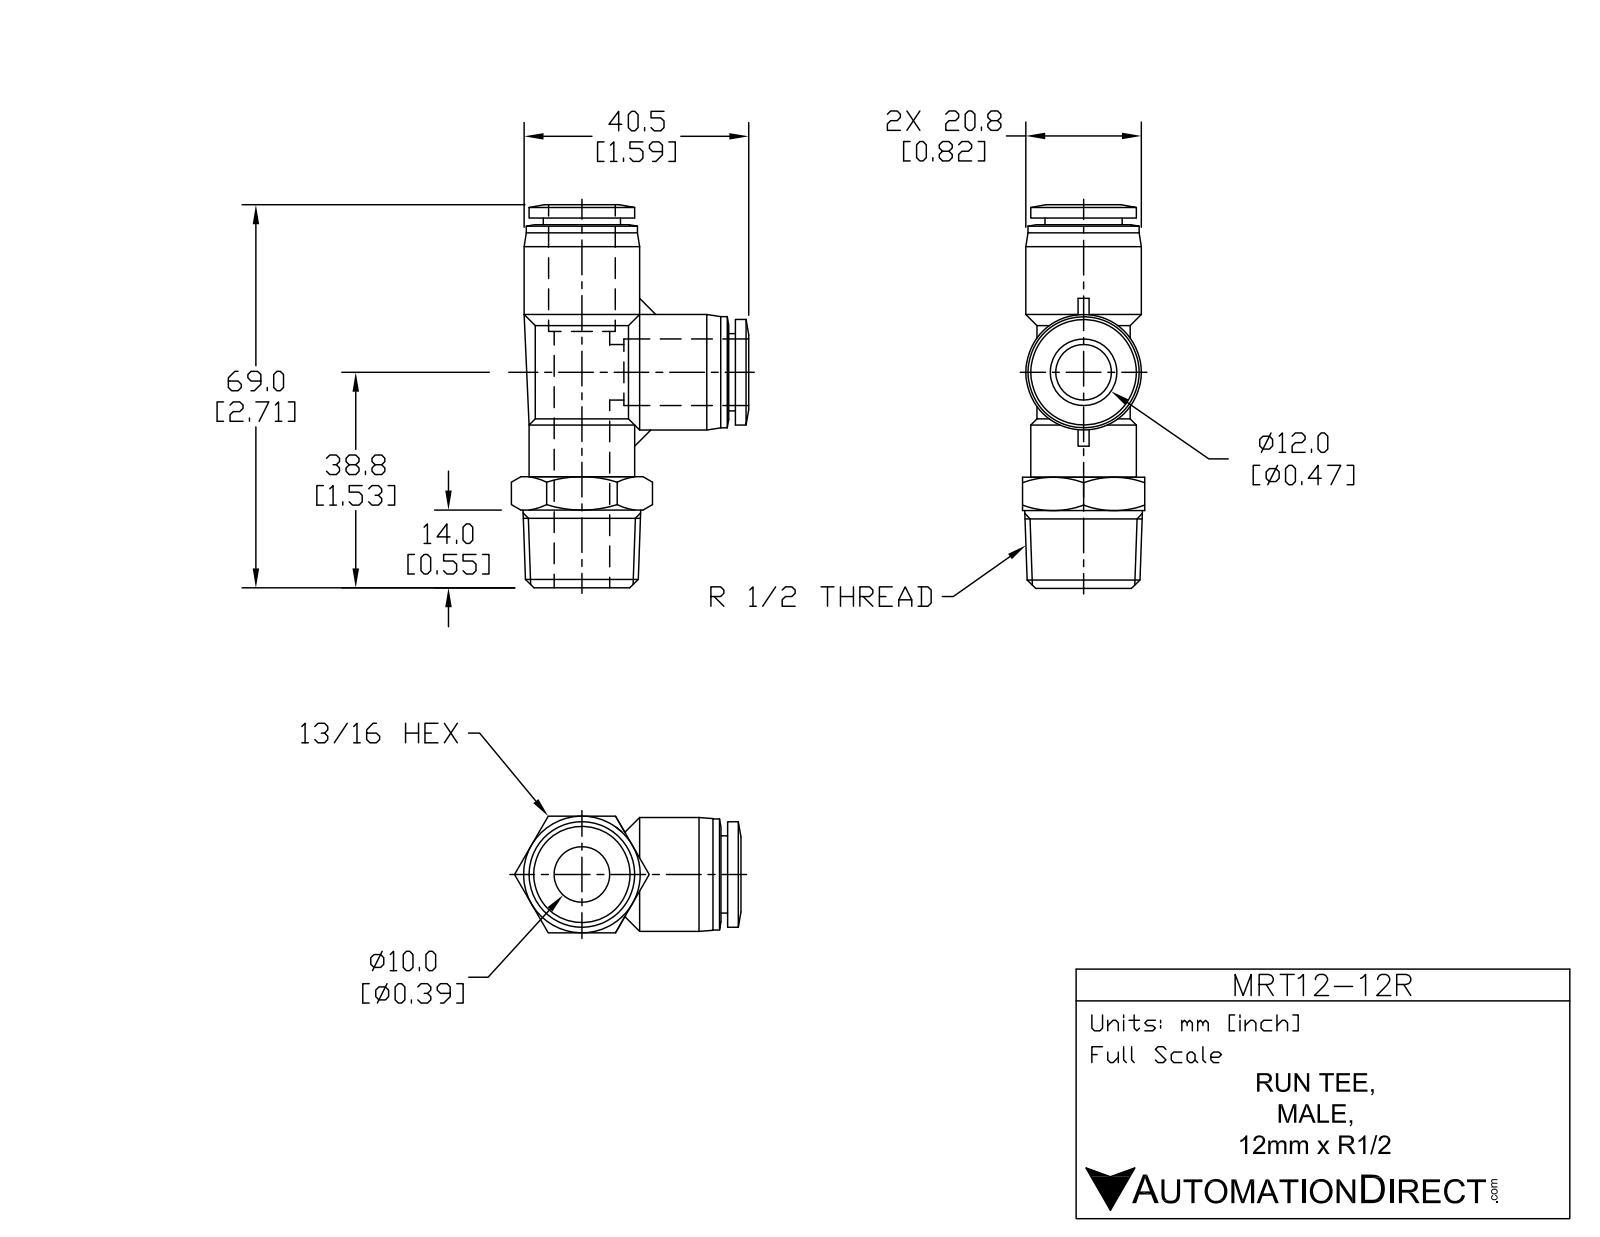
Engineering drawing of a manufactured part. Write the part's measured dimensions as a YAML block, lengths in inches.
part_name: "MRT12M-12R"
step_written_by: "SolidWorks 2015 (AUTOMOTIVE_DESIGN)"
units: inches
bodies: {solids: 1, faces: 99, planar: 24, cylindrical: 32, other: 43}
overall_size: [2.719, 1.664, 0.827]
volume: 1.113
surface_area: 15.61
round_holes:
  - {diameter: 0.394, count: 2}
  - {diameter: 0.484, count: 2}
round_bosses_or_shafts:
  - {diameter: 0.819, count: 2}
  - {diameter: 0.787, count: 2}
  - {diameter: 0.748, count: 2}
  - {diameter: 0.661, count: 2}
  - {diameter: 0.547, count: 2}
face_to_face_distances: [0.827, 0.047, 2.624, 0.76, 0.807, 0.374, 0.453, 2.577, 0.787, 1.789]
